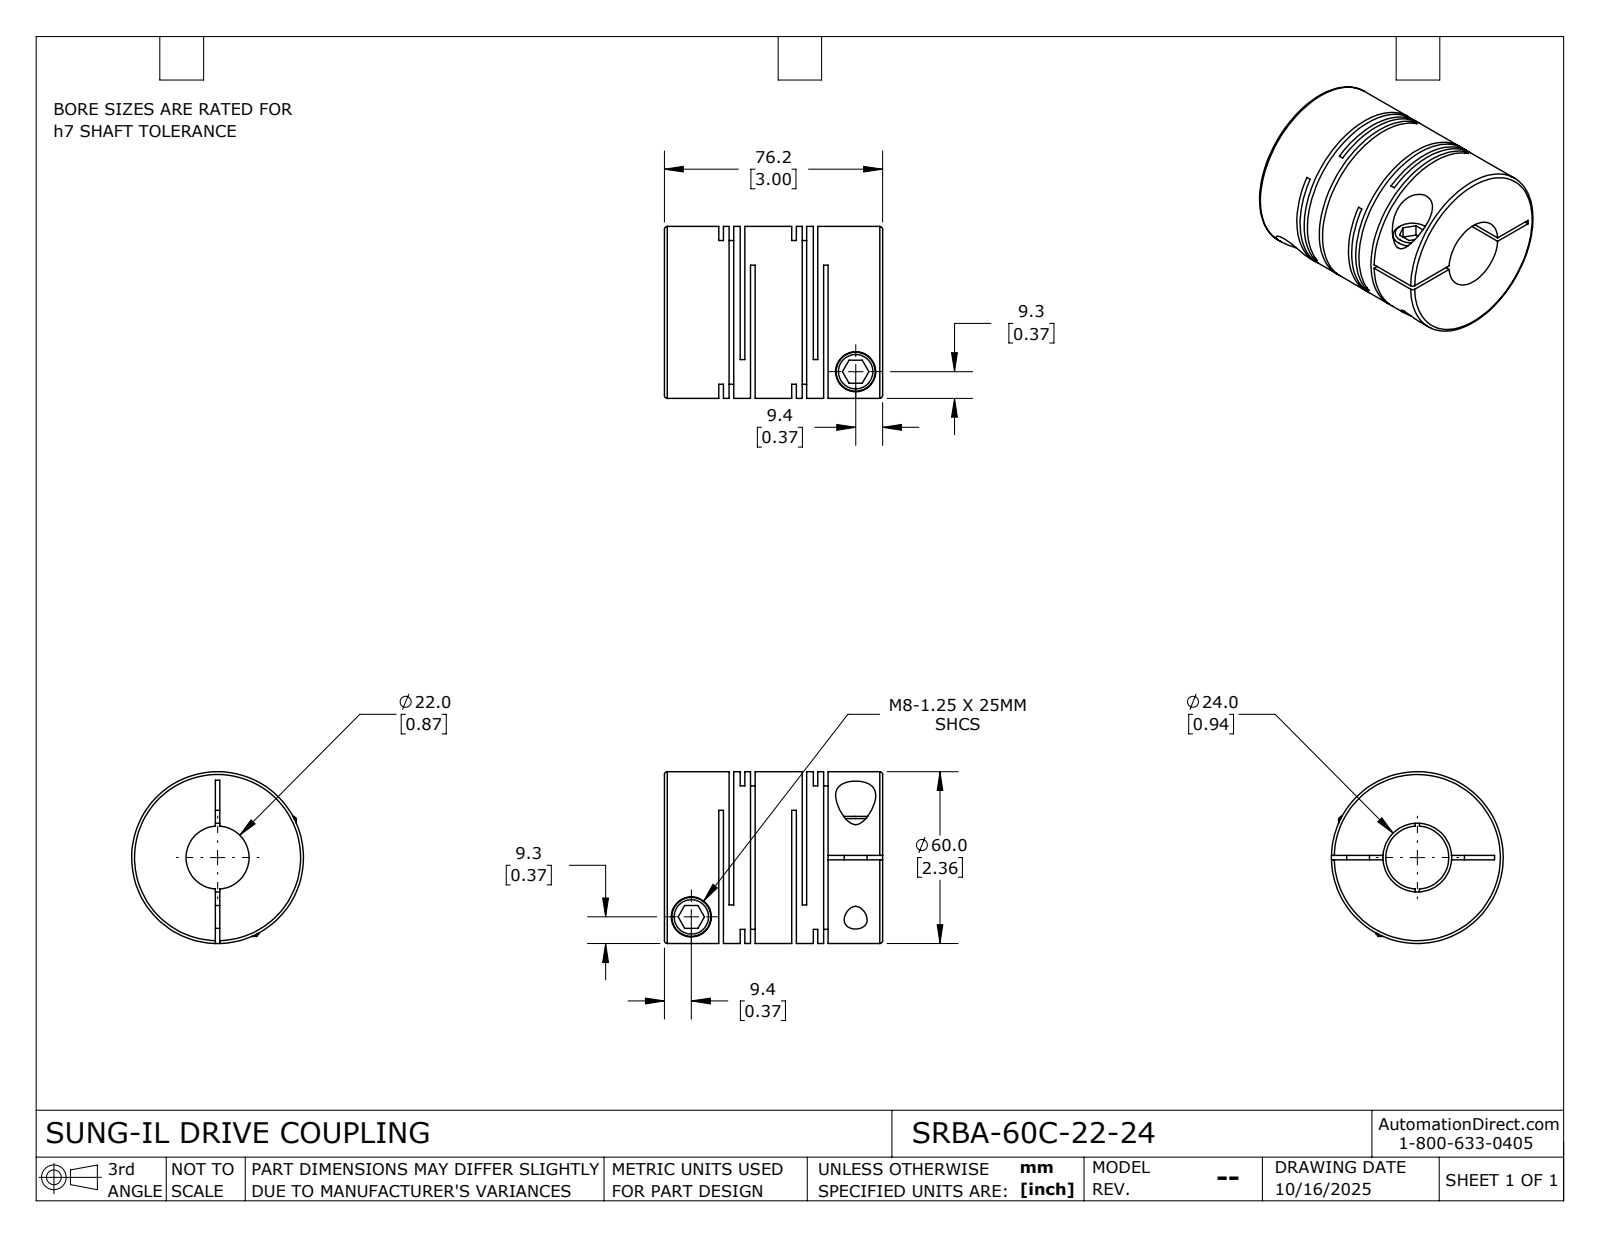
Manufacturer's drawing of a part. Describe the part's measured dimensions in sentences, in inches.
The part is named "SRBA-60C-22-24". Its 3-D file was written by "SolidWorks 2024 (CONFIG_CONTROL_DESIGN)". It is 1 solid with 115 faces: 60 planar, 42 cylindrical and 13 other. Overall it measures 3 by 2.362 by 2.362 inches. Its volume is 9.34 cubic inches and its surface area 88.73 square inches. Round holes: 2 of diameter 0.315, 2 of diameter 0.551, 1 of diameter 0.866, 1 of diameter 0.945. Round bosses or shafts: 2 of diameter 0.535, 1 of diameter 2.362. The main face-to-face distances are 0.063, 0.142, 0.295, 1.004, 1.299, 1.067, 0.079, 0.232, 0.941, 0.154.
